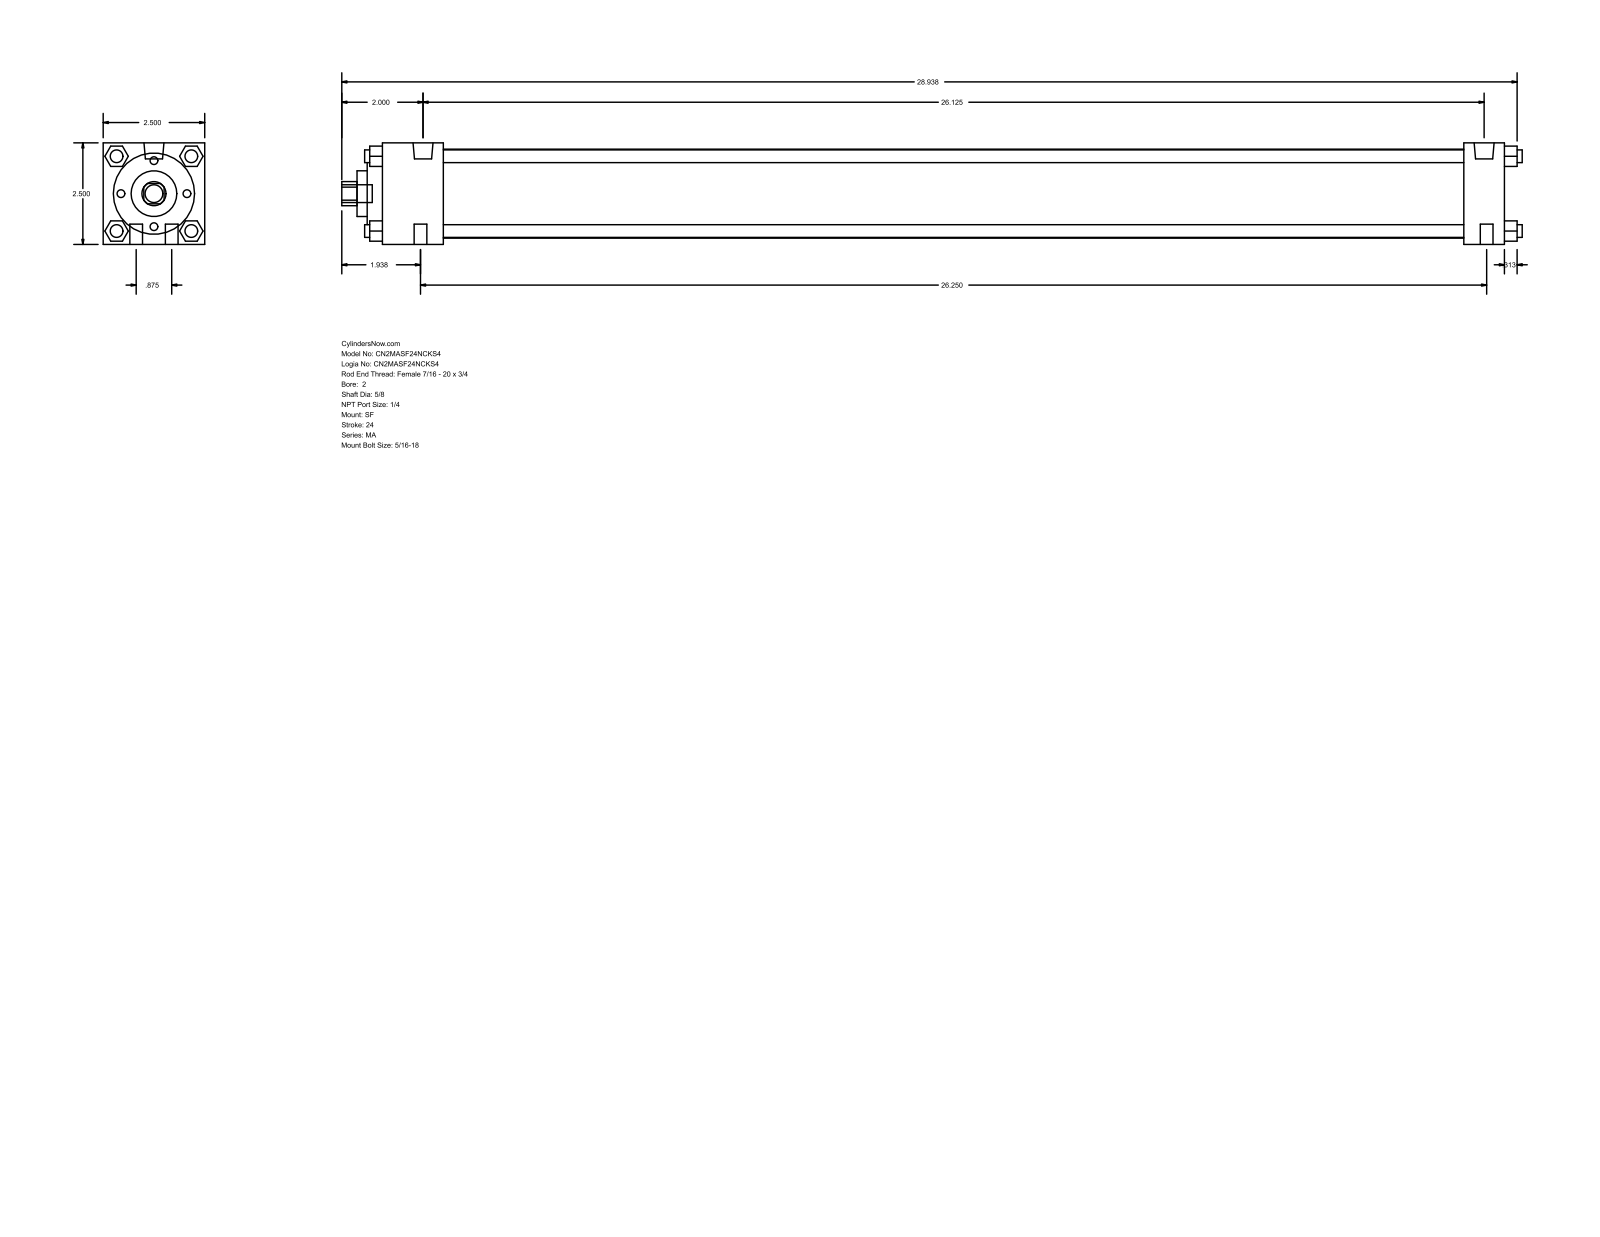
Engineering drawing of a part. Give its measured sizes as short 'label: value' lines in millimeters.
name: MA_SF__0200_0.625
written by: GSSL Pune (CONFIG_CONTROL_DESIGN)
unit: mm
bodies: 0 solids, 126 faces (95 planar, 31 cylindrical, 0 other)
size: 738.19 × 63.5 × 63.5
holes: 1× ⌀15.88, 1× ⌀28.57, 1× ⌀50.8, 1× ⌀55.63
bosses: 10× ⌀7.94, 2× ⌀12.49, 1× ⌀11.11
rounds: 1× R7.54
face distances: 63.5, 12.7, 38.1, 9.52, 701.68, 676.27, 25.41, 638.17, 663.58, 47.62
